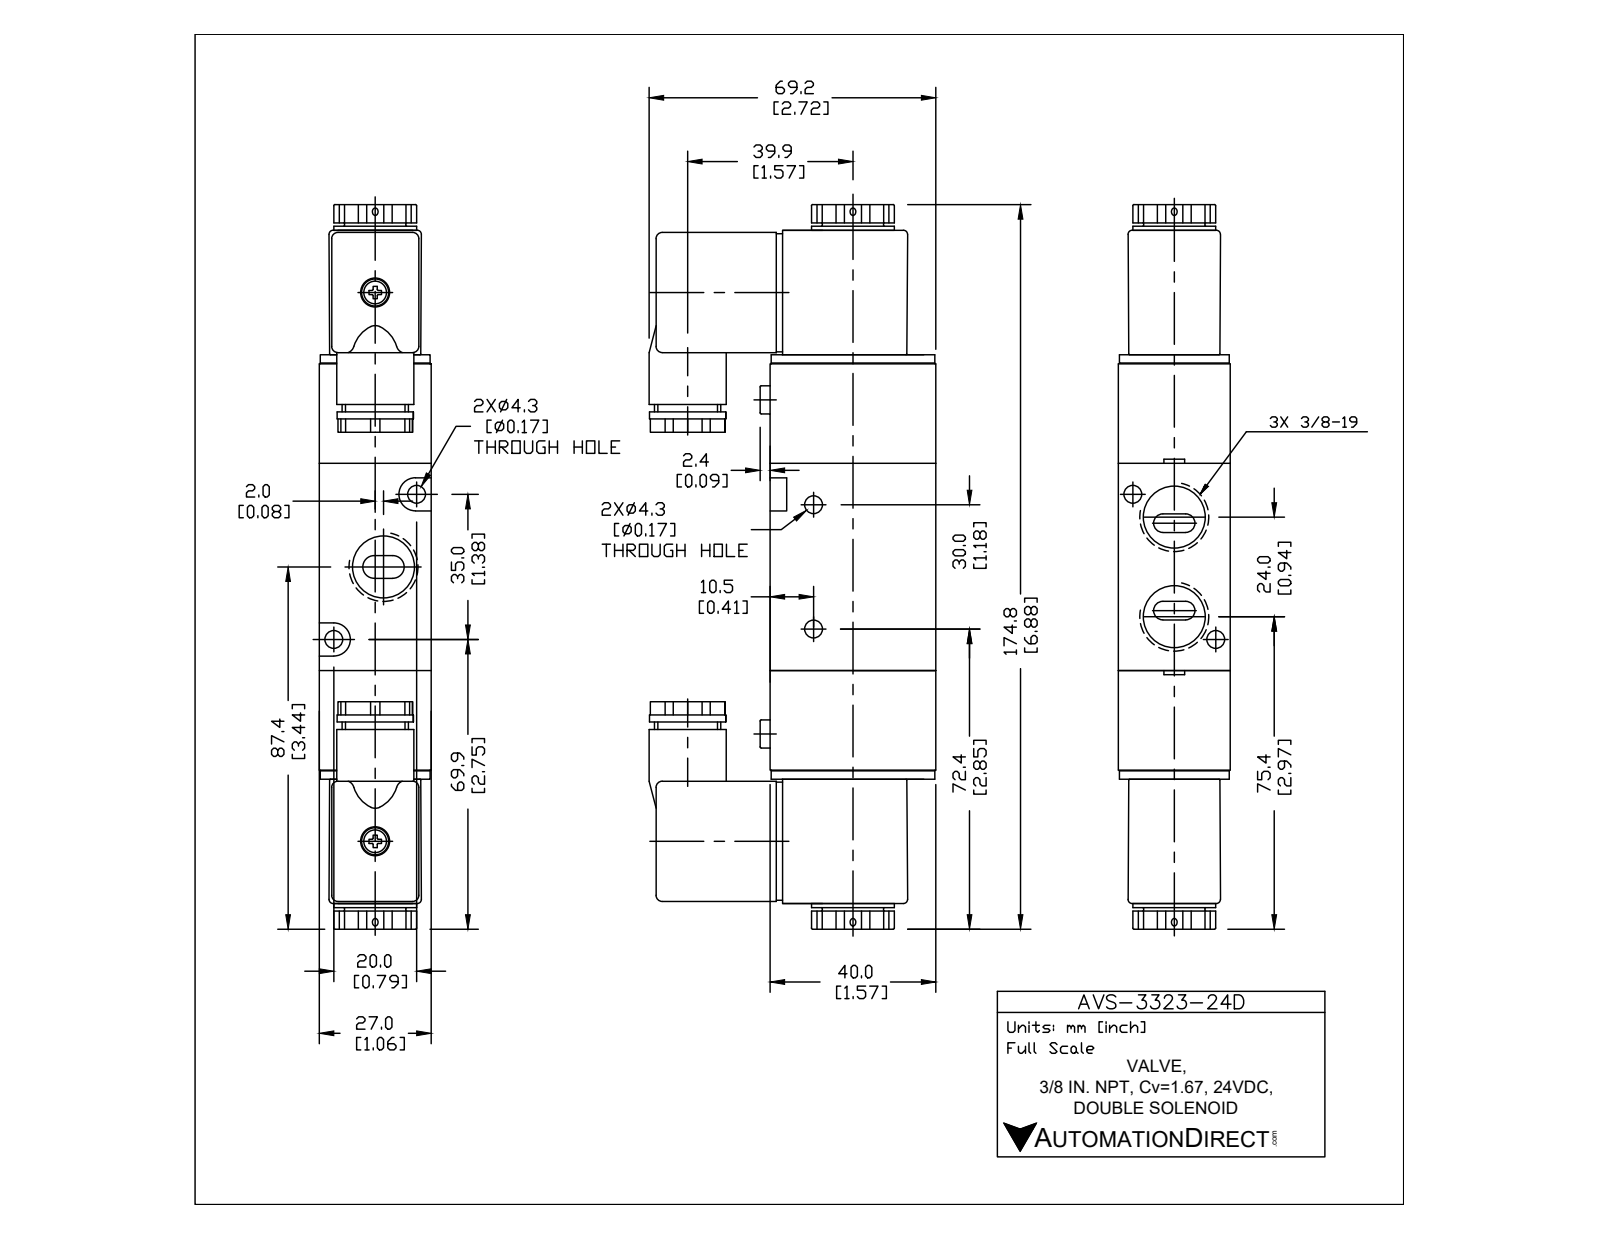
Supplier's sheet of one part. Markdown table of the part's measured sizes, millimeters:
| quantity | value |
| --- | --- |
| part name | AVS-3323-24D |
| STEP written by | SolidWorks 2015 (CONFIG_CONTROL_DESIGN) |
| units | millimeters |
| bodies | 5 solids, 246 faces (132 planar, 82 cylindrical, 32 other) |
| overall size | 174.8 × 69.1 × 27 |
| volume | 188 123 mm³ |
| surface area | 40 469 mm² |
| round holes (diameter × count) | 4.3 × 4, 14.27 × 3, 9.3 × 1 |
| round bosses / shafts (diameter × count) | 6.8 × 2, 20 × 1, 18.6 × 1, 18.4 × 1, 16 × 1, 14.8 × 1 |
| partial cylindrical surfaces (radius × count) | 1 × 20, 0.5 × 12, 4 × 2 |
| main face-to-face distances | 3, 24, 50, 27.45, 27, 21, 25.19, 2.26, 2.27, 22.92 |
| hole center spacings | 11.41, 12.17, 31.15, 19.24, 21.22, 24, 30, 40.31 |
